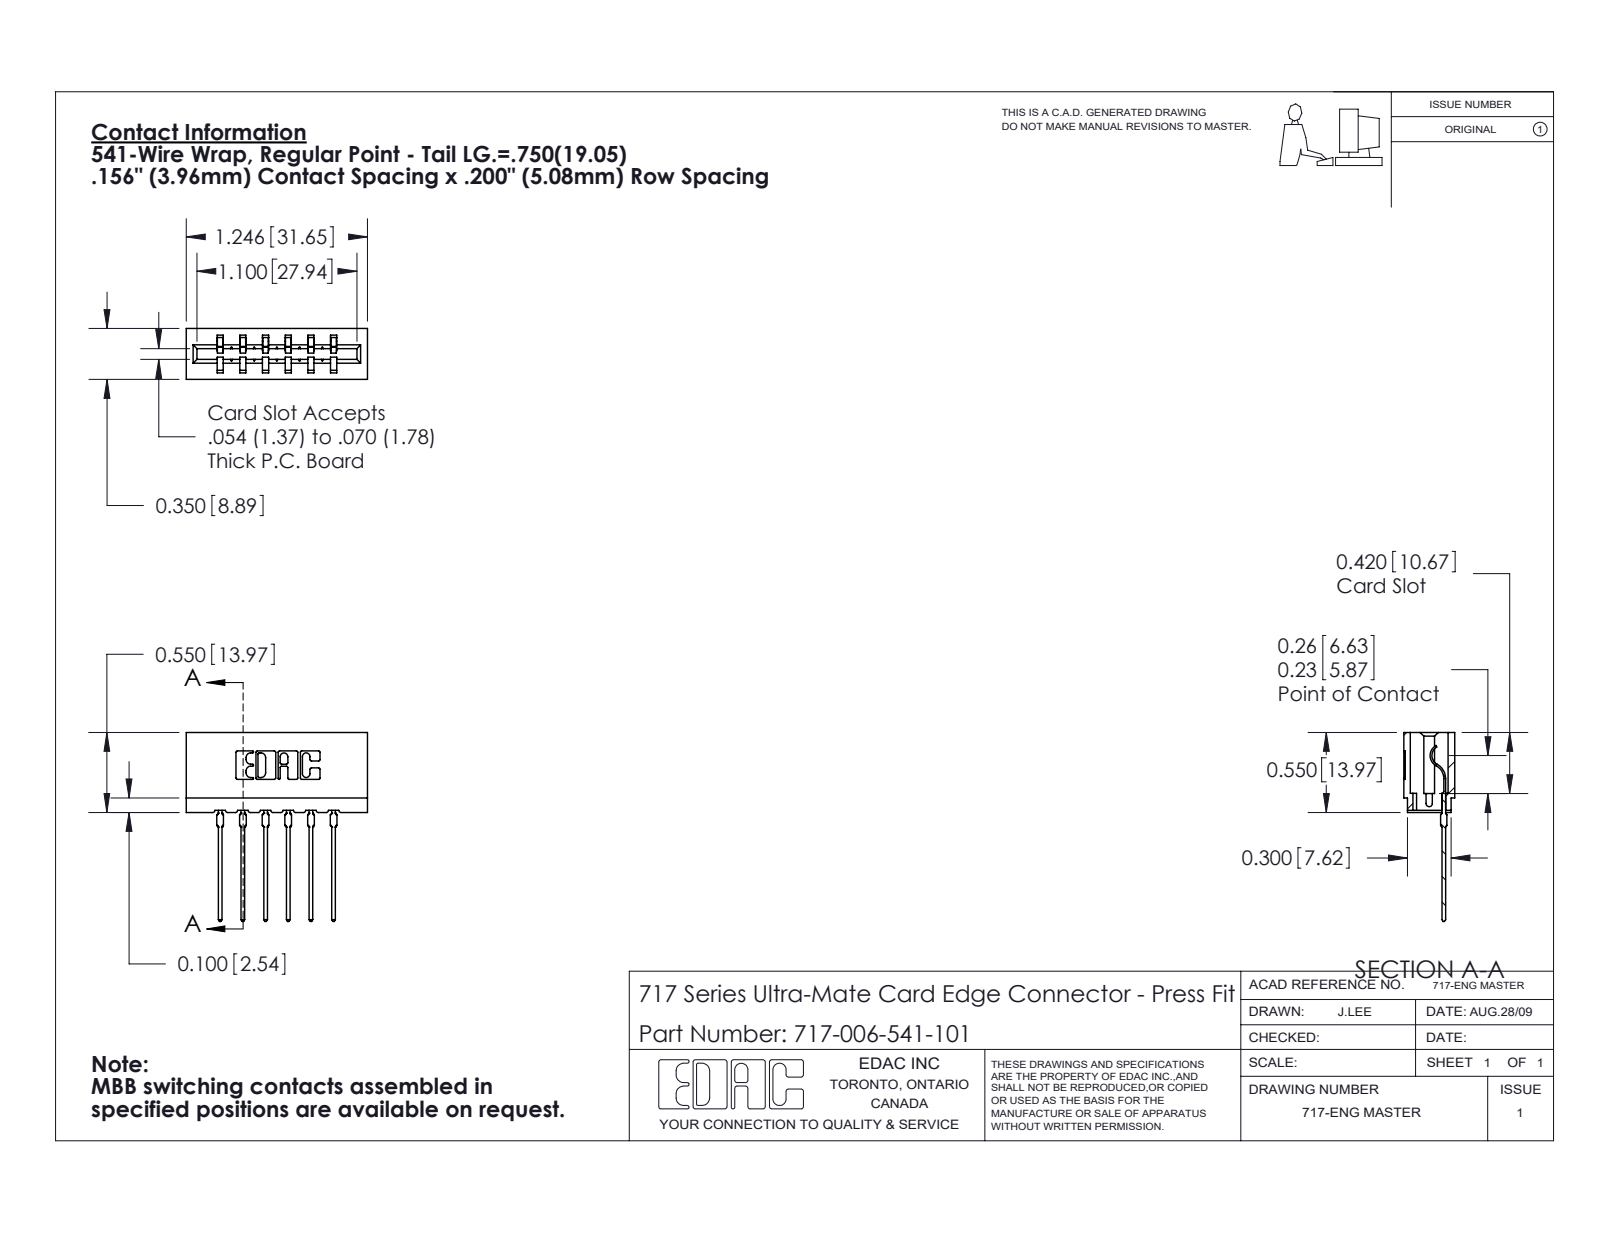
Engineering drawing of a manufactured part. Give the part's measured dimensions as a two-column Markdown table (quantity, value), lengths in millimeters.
| quantity | value |
| --- | --- |
| part name | 717-006-541-101; 717 Part_Insulator Option - 06; 745-292-001_541 |
| STEP written by | SolidWorks 2020 (CONFIG_CONTROL_DESIGN) |
| units | millimeters |
| bodies | 7 solids, 772 faces (462 planar, 154 cylindrical, 156 other) |
| overall size | 33 × 31.6 × 8.9 |
| volume | 2 870 mm³ |
| surface area | 3 754 mm² |
| partial cylindrical surfaces (radius × count) | 0.3 × 22, 0.4 × 12, 0.5 × 12, 0.2 × 6, 0.8 × 6, 0.1 × 4, 0.3 × 4, 0.7 × 3 |
| main face-to-face distances | 5.4, 4, 3.5, 8.9, 5, 7.9, 15.8, 1.1, 7.9, 11.9 |
